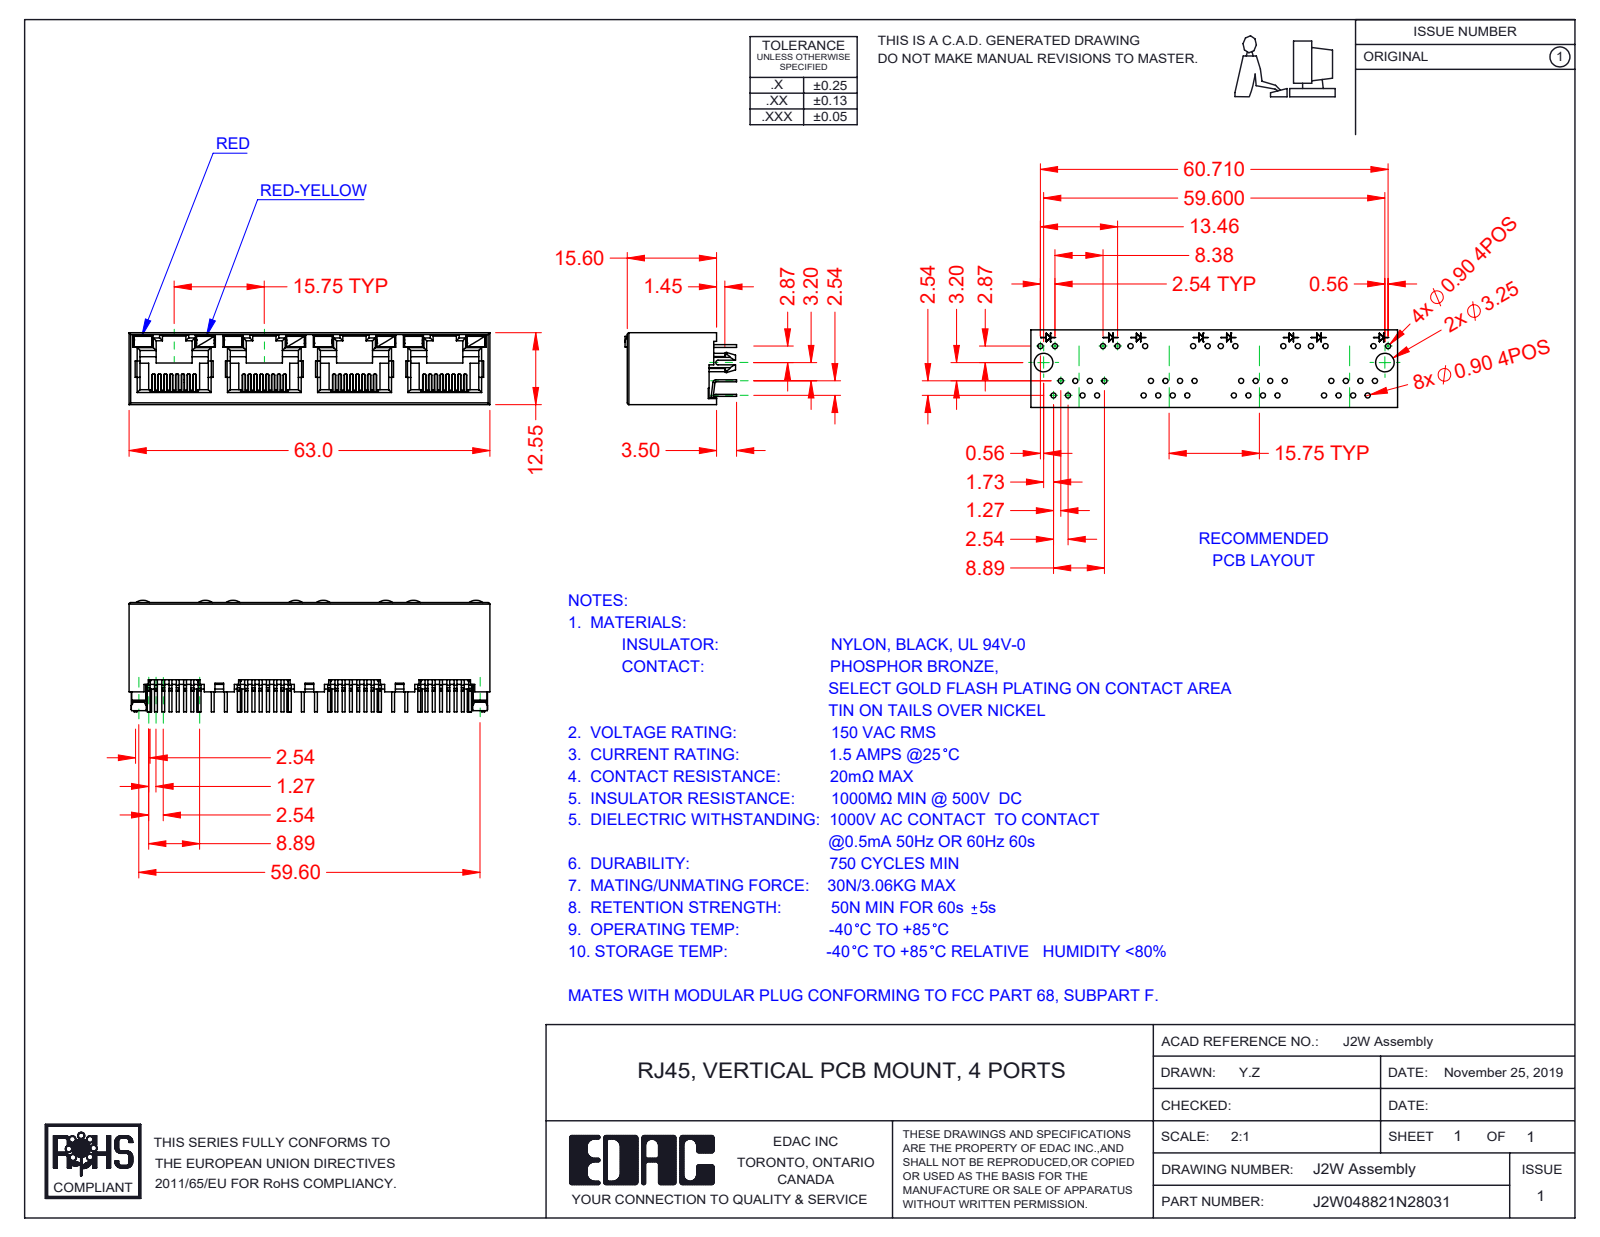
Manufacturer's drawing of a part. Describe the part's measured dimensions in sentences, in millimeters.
The part is named "2W LED RH_8-Red-Yellow; 2W Insulator; 2W Contact Lock; J2W048821N28031 (+2 more)". Its 3-D file was written by "SolidWorks 2020 (CONFIG_CONTROL_DESIGN)". It is 45 solids with 3139 faces: 2600 planar, 481 cylindrical and 58 other. Overall it measures 63 by 19.5 by 12.55 millimeters. Its volume is 5 335 cubic millimeters and its surface area 13 144 square millimeters. Partial cylindrical surfaces (rounded edges, fillets, slot ends): 64 of radius 0.15, 29 of radius 0.2, 28 of radius 0.5, 14 of radius 0.3, 8 of radius 0.45, 8 of radius 2, 2 of radius 0.25, 2 of radius 1.5. The main face-to-face distances are 12.55, 11.9, 0.65, 15.75, 0.36, 1.5, 0.78, 0.6, 11.3, 31.5.
